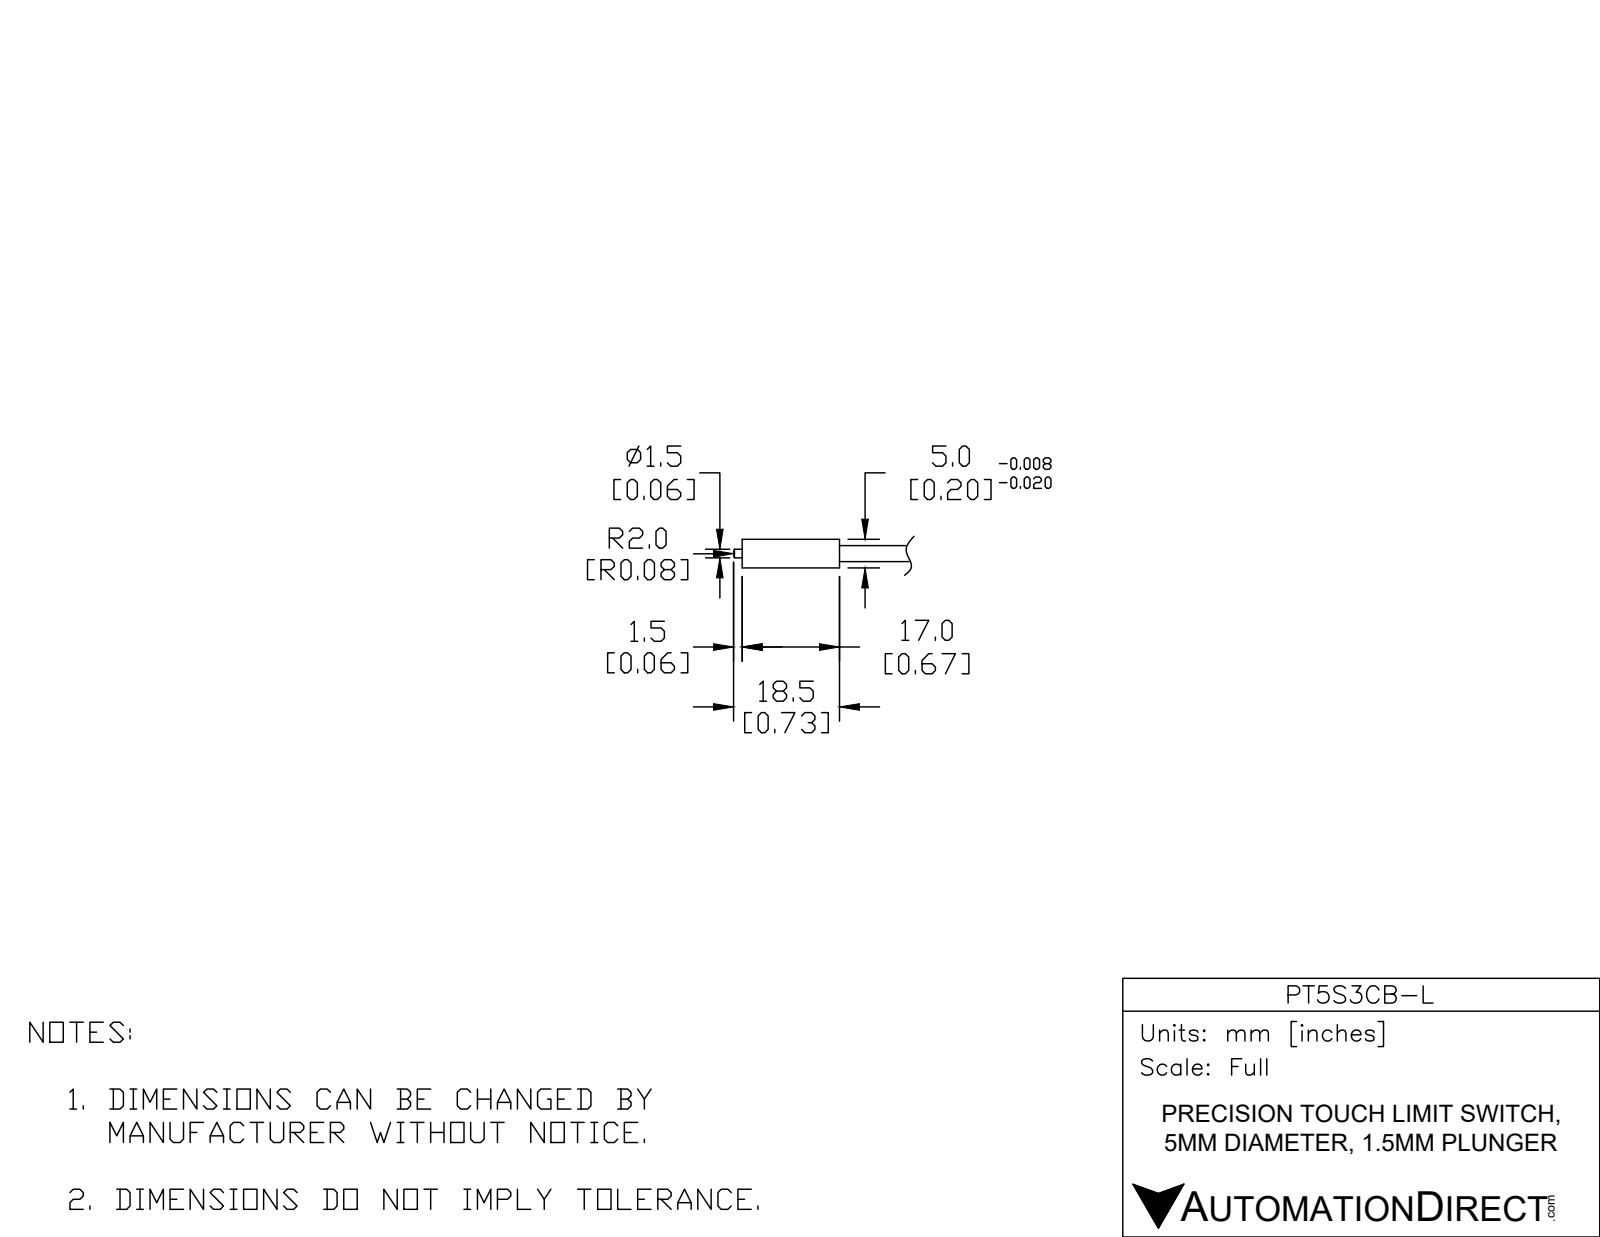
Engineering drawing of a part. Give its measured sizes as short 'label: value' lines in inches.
written by: Spatial InterOp 3D (CONFIG_CONTROL_DESIGN)
unit: in
bodies: 2 solids, 21 faces (7 planar, 12 cylindrical, 2 other)
size: 6.831 × 0.197 × 0.197
volume: 0.096 in³; area: 2.871 in²
bosses: 1× ⌀0.197, 1× ⌀0.189, 1× ⌀0.11, 1× ⌀0.059
face distances: 0.669, 5.394, 6.378, 4.724, 5.709, 0.984, 3.091, 3.169, 6.772, 2.421
